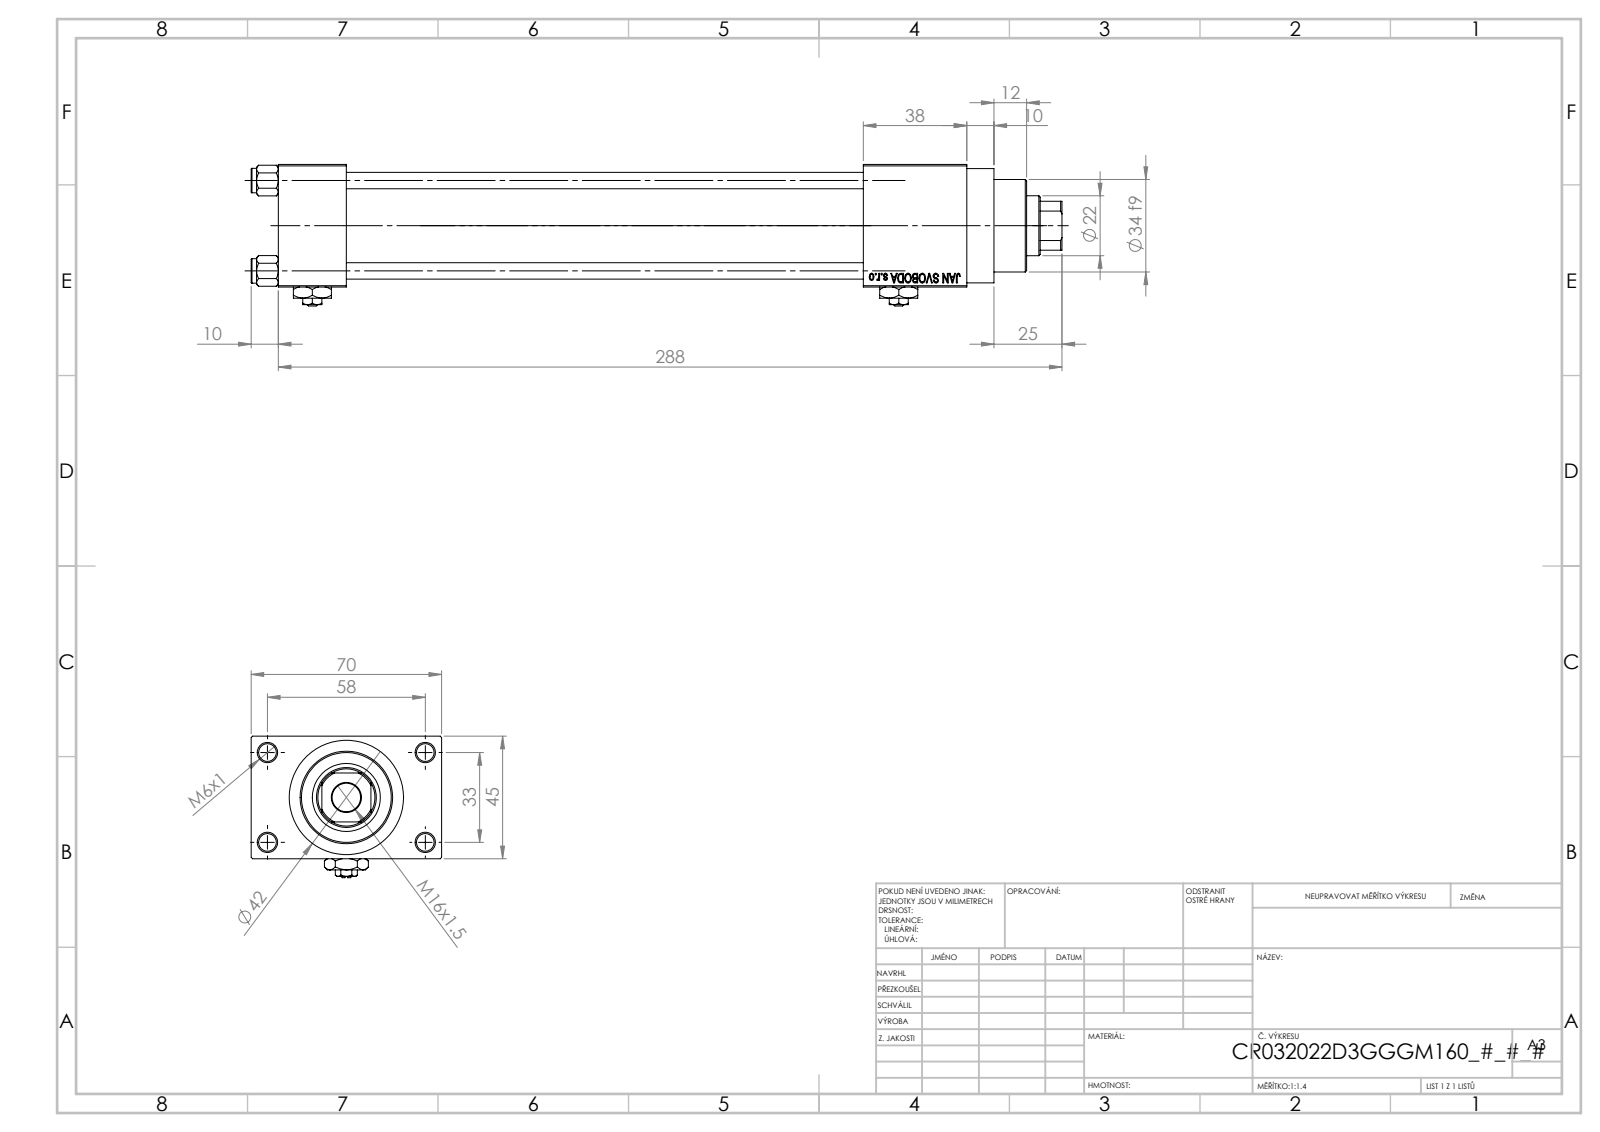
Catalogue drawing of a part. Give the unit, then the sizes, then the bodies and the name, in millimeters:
Units: millimetres
Overall size (bounding box): 298 × 70 × 52
Round holes (diameter × count): ⌀6 ×4, ⌀6.5 ×4, ⌀7 ×2, ⌀13.16 ×2, ⌀20 ×2, ⌀10.5 ×1, ⌀22 ×1, ⌀24 ×1, ⌀25 ×1, ⌀32 ×1, ⌀33 ×1
Round bosses / shafts (diameter × count): ⌀9 ×4, ⌀42 ×1, ⌀38 ×1, ⌀34 ×1
Partial cylindrical surfaces — rounded edges, fillets, slot ends (radius × count): R10.5 ×1
Main face-to-face distances: 45, 25, 12.5, 57.5, 190, 215, 228, 38, 70, 253
Hole centre spacings: 12.4, 23.48, 33.2, 33.37, 35.35, 45.6, 56.35, 33
Volume: 358 601 mm³ · Surface area: 132 220 mm²
Bodies: 13 solids, 1202 faces (542 planar, 100 cylindrical, 560 other)
Part name (STEP PRODUCT): Zatka_pro_OIL_PORT; V215_VC_A; V215CR_VCP_D; NUT_M5_D (+2 more)
STEP written by: SolidWorks 2019 (CONFIG_CONTROL_DESIGN)
